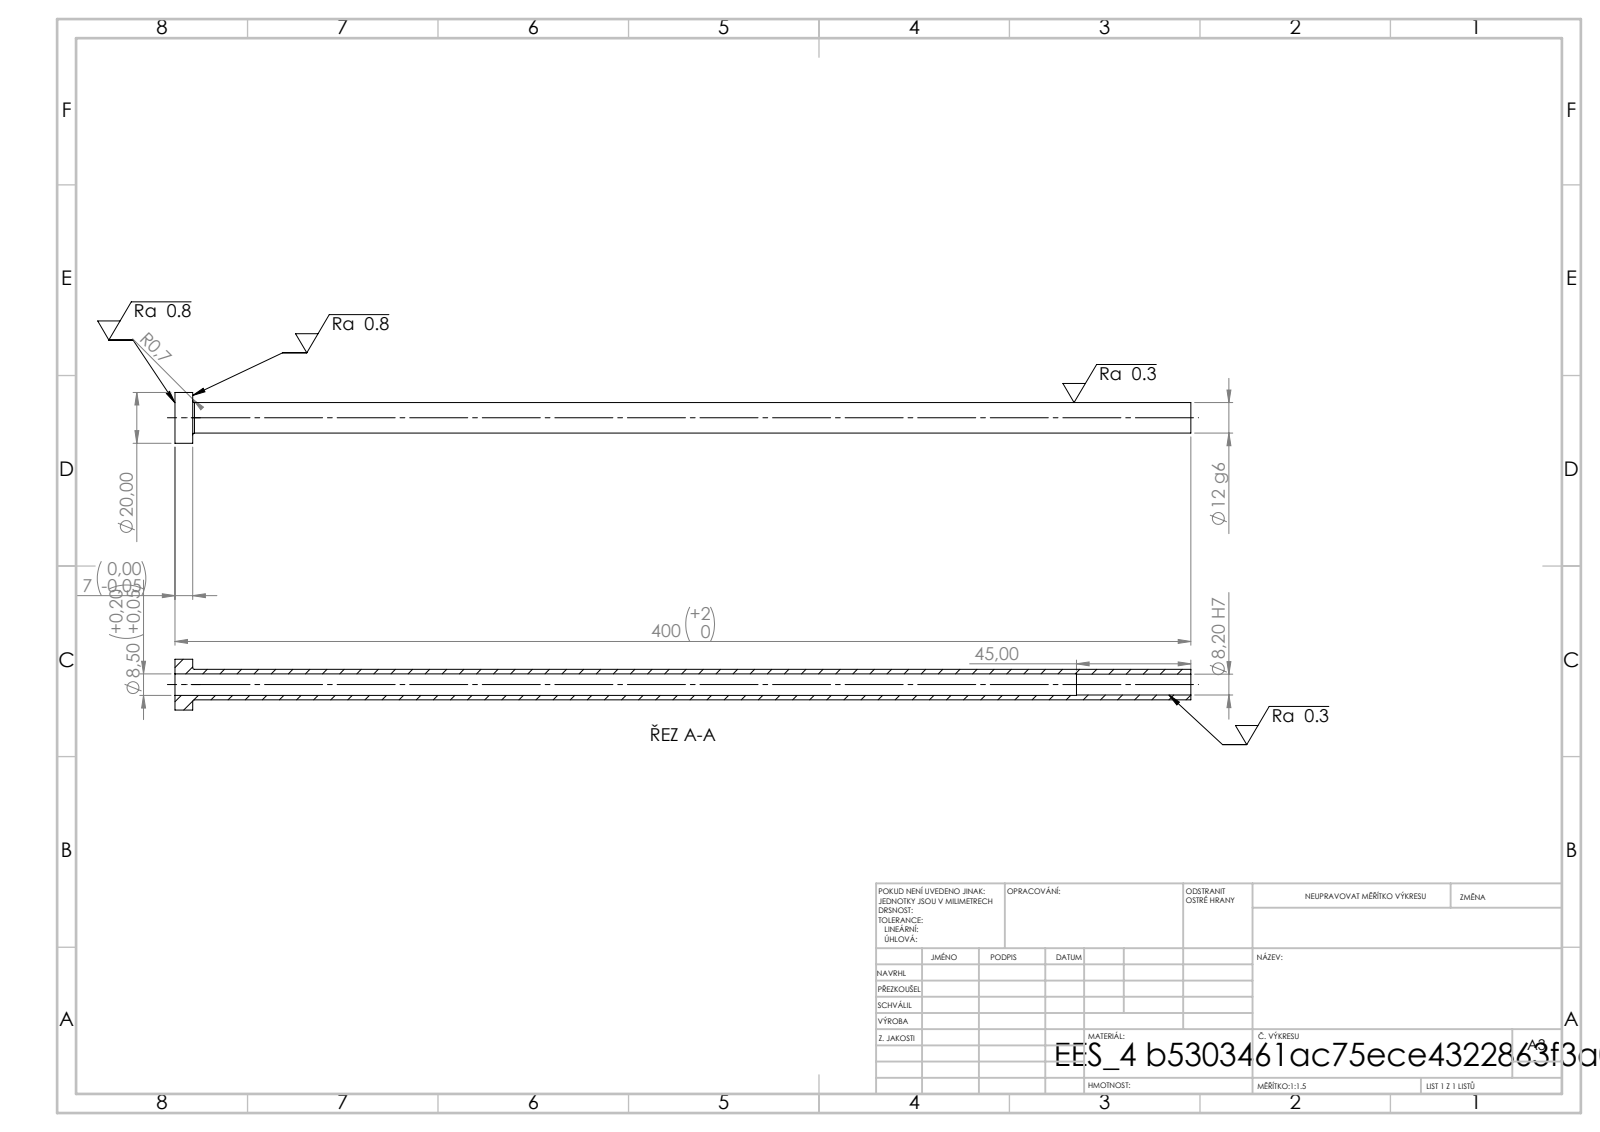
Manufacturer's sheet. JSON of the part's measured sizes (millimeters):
{"step_written_by": "SolidWorks 2019 (CONFIG_CONTROL_DESIGN)", "units": "millimeters", "bodies": {"solids": 1, "faces": 14, "planar": 4, "cylindrical": 8, "other": 2}, "overall_size": [400, 20, 20], "volume_mm3": 24129, "surface_area_mm2": 26406, "round_holes": [[8.2, 1], [8.5, 1]], "round_bosses_or_shafts": [[20, 1], [12, 1]], "face_to_face_distances": [7, 400, 393, 355, 348, 45]}
